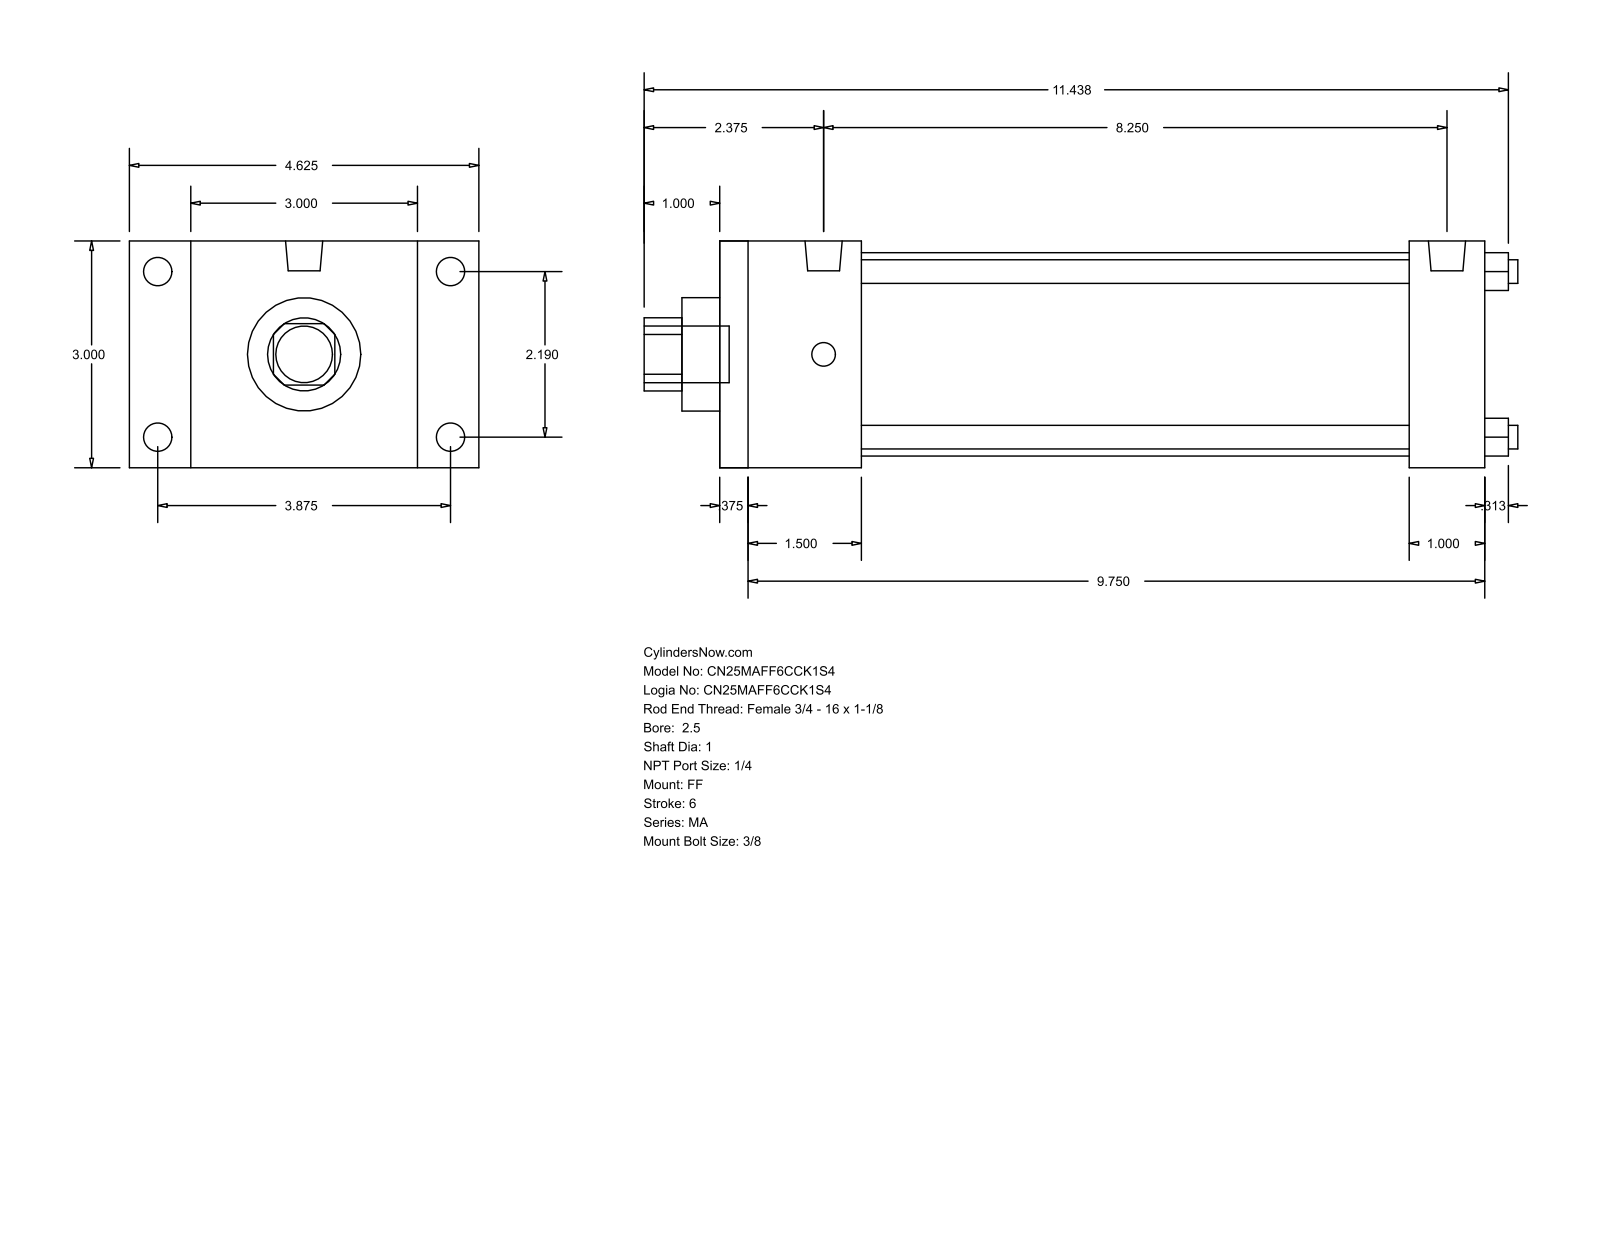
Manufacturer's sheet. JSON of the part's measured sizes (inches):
{"part_name": "MA_FF__0250_1", "step_written_by": "GSSL Pune (CONFIG_CONTROL_DESIGN)", "units": "inches", "bodies": {"solids": 0, "faces": 92, "planar": 64, "cylindrical": 28, "other": 0}, "overall_size": [11.563, 4.625, 3], "round_holes": [[0.313, 4], [1, 1], [1.5, 1], [2.69, 1]], "round_bosses_or_shafts": [[0.375, 4], [0.313, 4], [0.492, 2], [0.75, 1]], "partial_cylinders_radius": [[0.484, 1]], "face_to_face_distances": [3, 10.125, 9.75, 0.375, 1, 1.875, 9.125, 1.5, 8.75, 7.25], "hole_center_spacings": [1.548, 2.19, 3.097]}
